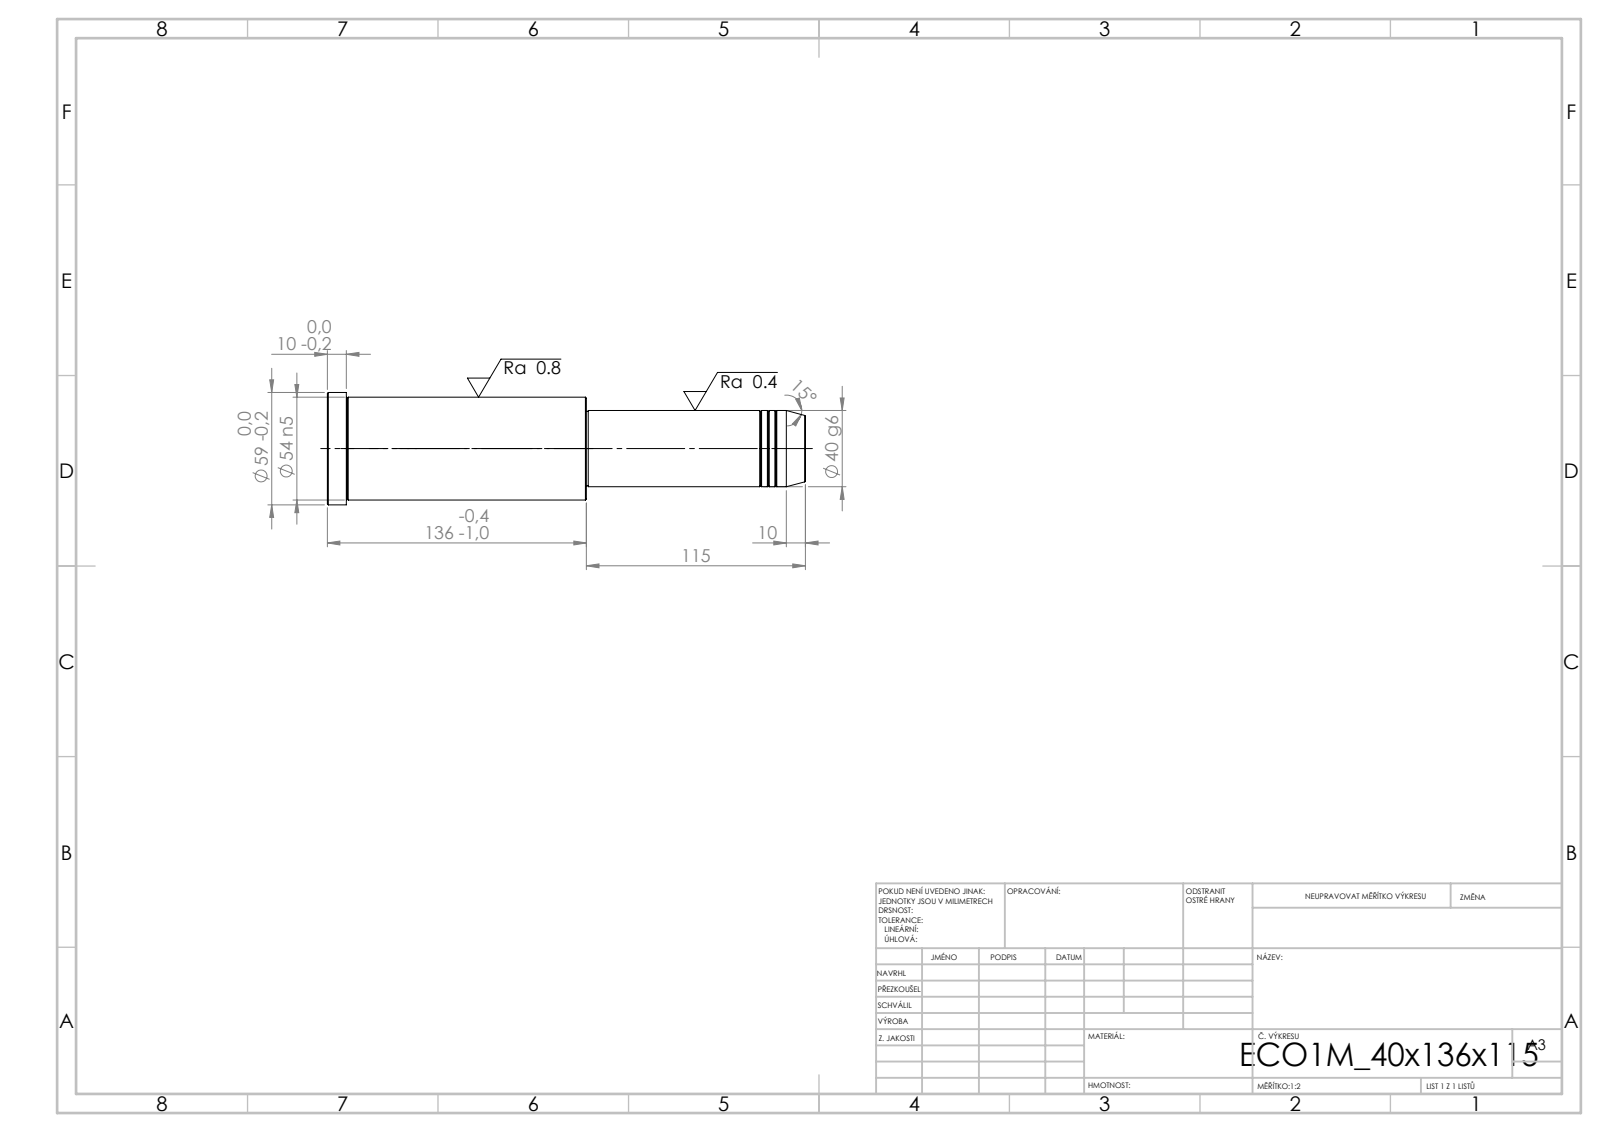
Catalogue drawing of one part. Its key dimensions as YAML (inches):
step_written_by: "SolidWorks 2019 (CONFIG_CONTROL_DESIGN)"
units: inches
bodies: {solids: 1, faces: 43, planar: 5, cylindrical: 14, other: 24}
overall_size: [9.882, 2.323, 2.323]
volume: 27.98
surface_area: 66.8
round_bosses_or_shafts:
  - {diameter: 2.323, count: 1}
  - {diameter: 2.126, count: 1}
  - {diameter: 1.575, count: 1}
  - {diameter: 1.535, count: 1}
face_to_face_distances: [5.354, 4.528, 9.882, 9.488, 4.961, 0.394, 4.488, 0.039, 5, 5.394]
